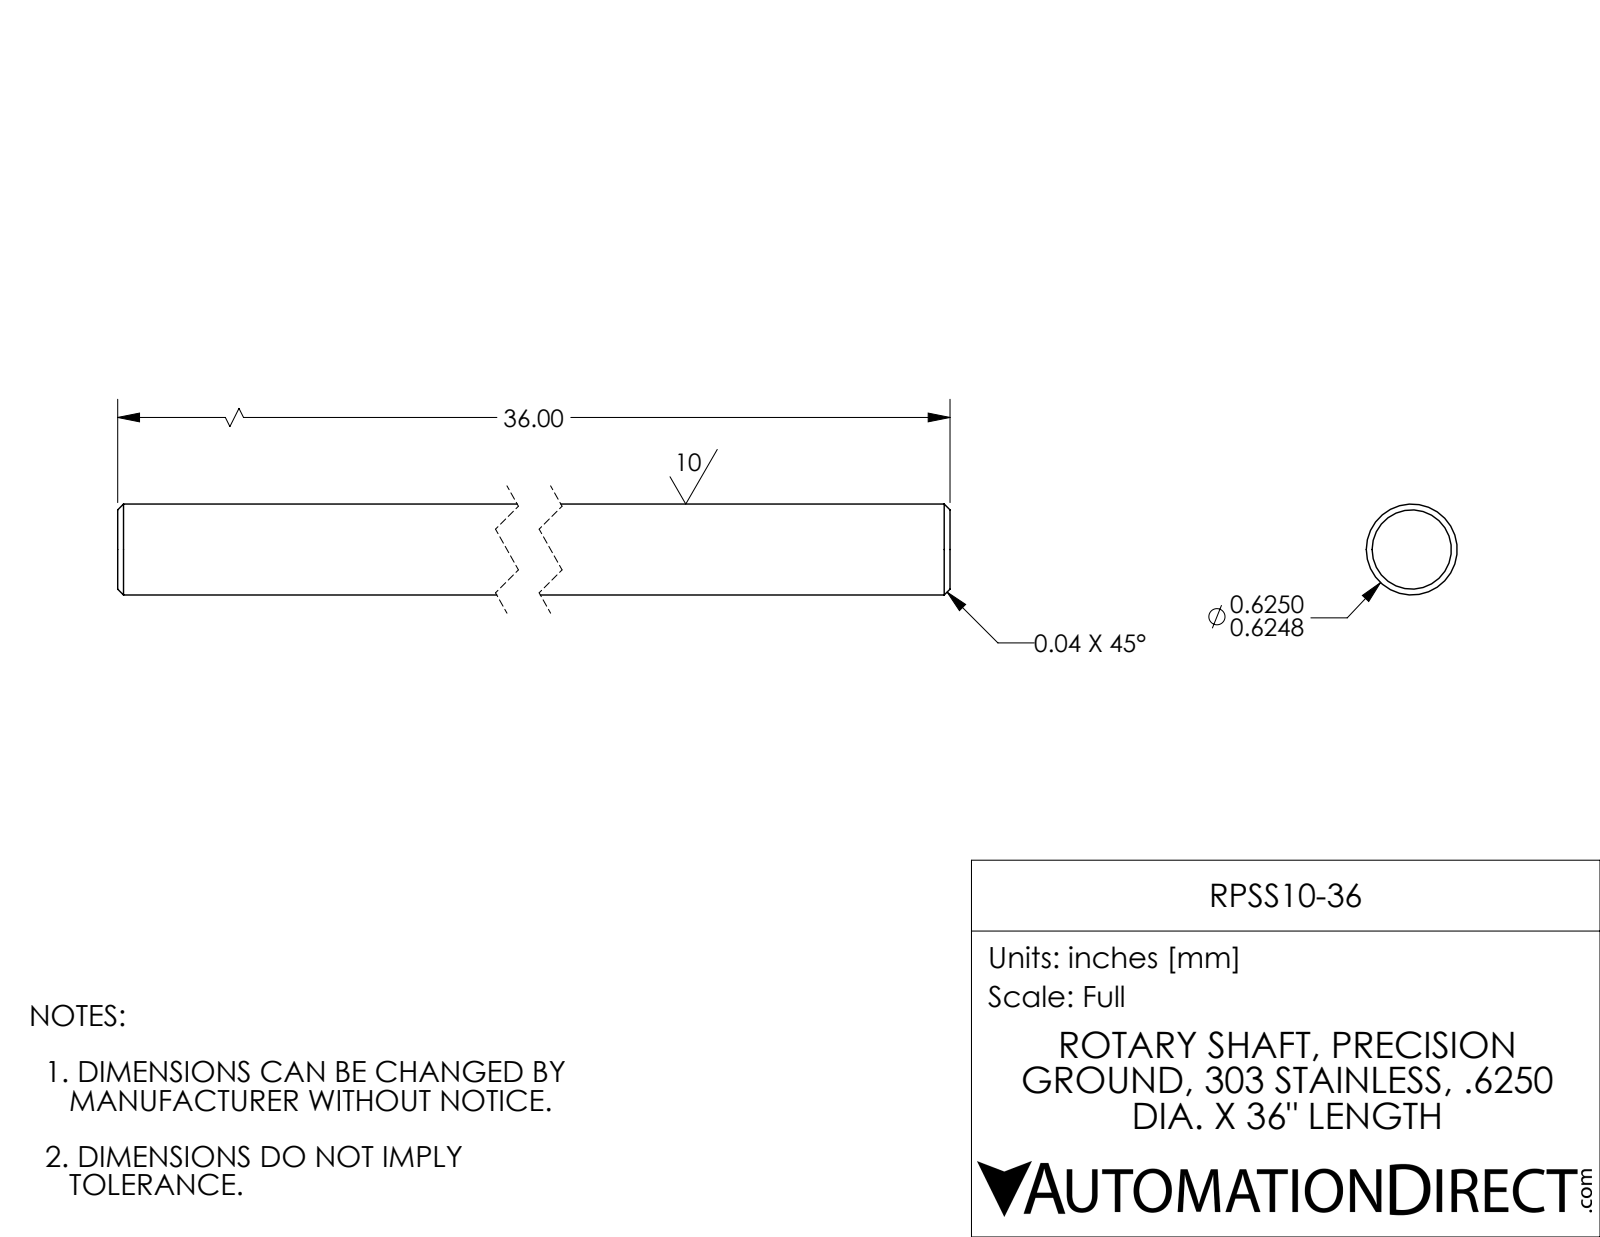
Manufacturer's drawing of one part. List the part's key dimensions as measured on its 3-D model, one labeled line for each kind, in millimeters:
Part name (STEP PRODUCT): RPSS10-36
STEP written by: SolidWorks 2017 (AUTOMOTIVE_DESIGN)
Units: millimetres
Bodies: 1 solid, 8 faces (2 planar, 2 cylindrical, 4 other)
Overall size (bounding box): 914.4 × 15.9 × 15.9
Volume: 180 900 mm³ · Surface area: 45 940 mm²
Round bosses / shafts (diameter × count): ⌀15.9 ×1
Main face-to-face distances: 914.4
